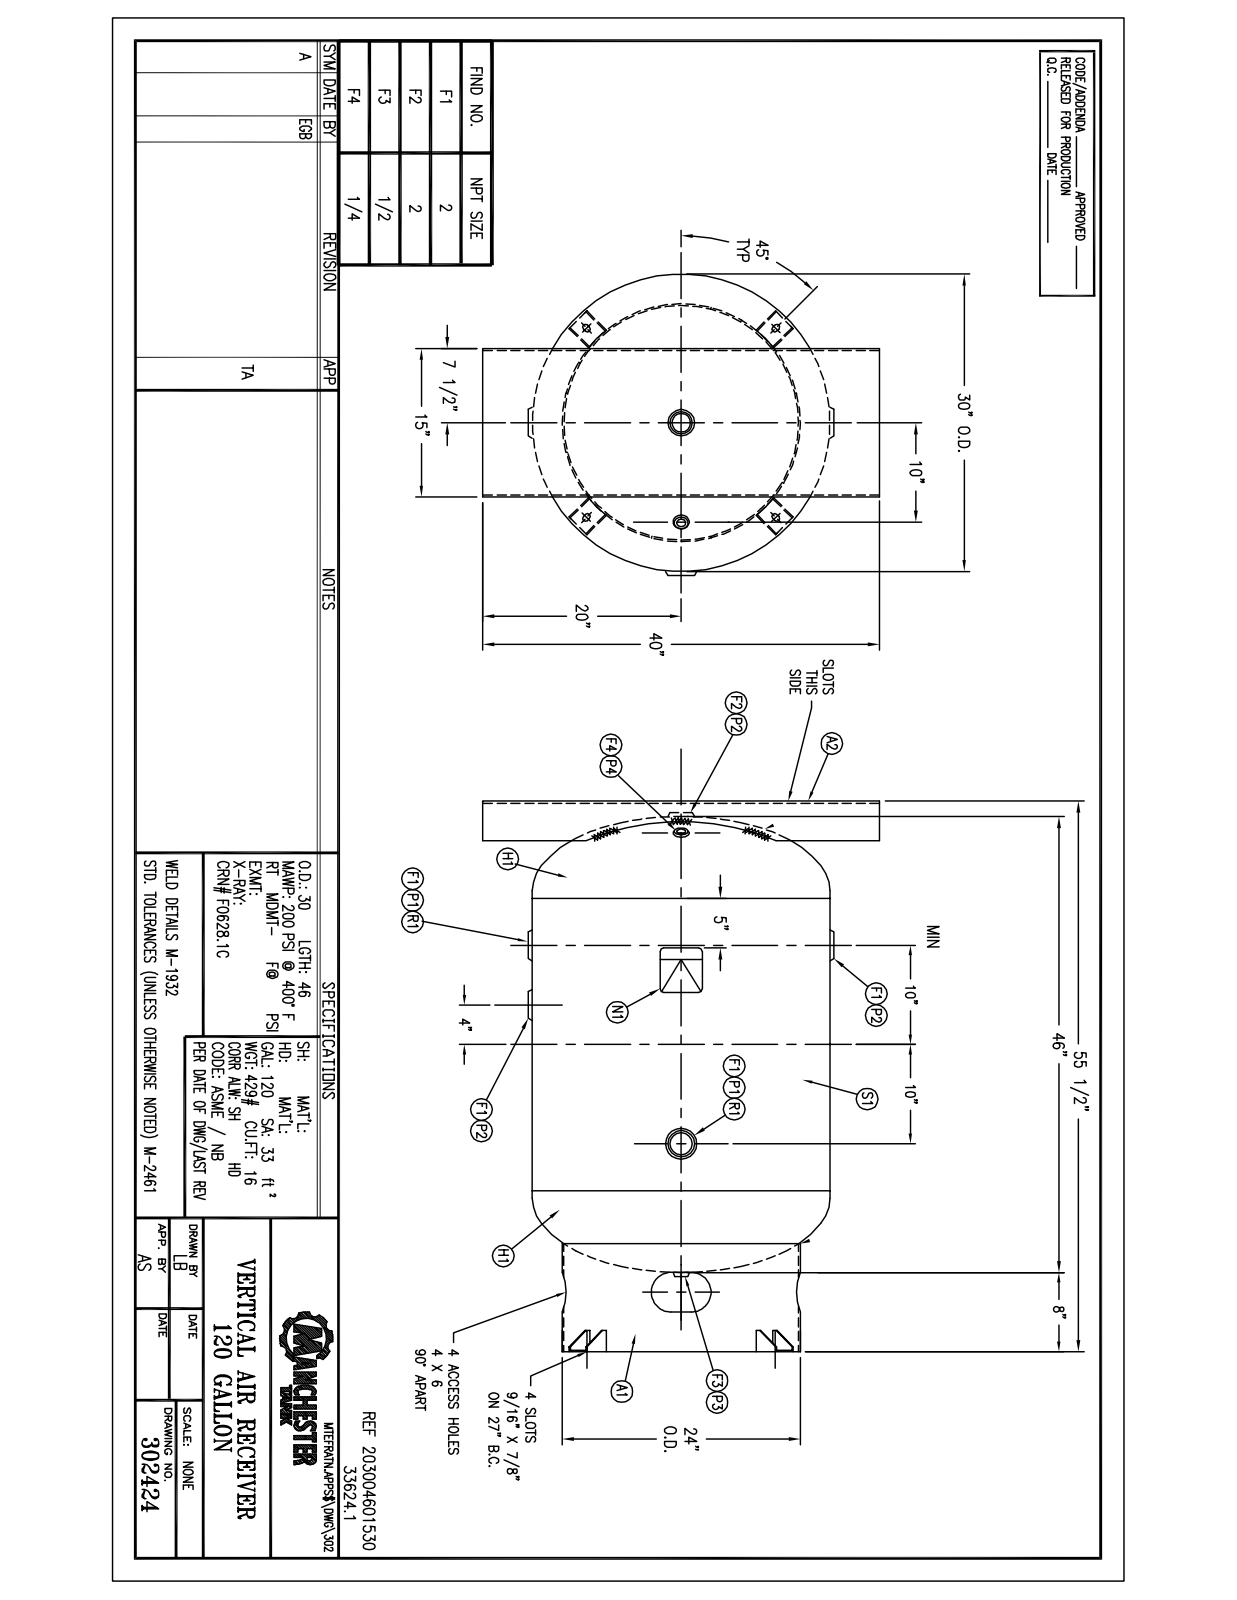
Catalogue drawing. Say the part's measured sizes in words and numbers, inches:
The part is named "302424". Its 3-D file was written by "SolidWorks 2011 (CONFIG_CONTROL_DESIGN)". It is 0 solids with 288 faces: 112 planar, 98 cylindrical and 78 other. Overall it measures 55.213 by 40 by 30.842 inches. Round holes: 2 of diameter 2.375, 2 of diameter 2.375, 1 of diameter 0.54, 1 of diameter 1, 1 of diameter 3.5, 1 of diameter 23.638, 1 of diameter 29.546. Round bosses or shafts: 3 of diameter 3.625, 1 of diameter 30, 1 of diameter 29.63, 1 of diameter 24, 1 of diameter 2.875, 1 of diameter 1.5. Partial cylindrical surfaces (rounded edges, fillets, slot ends): 10 of radius 0.266, 8 of radius 0.25, 8 of radius 0.281, 8 of radius 0.384, 2 of radius 0.094, 2 of radius 0.312, 2 of radius 0.344, 1 of radius 15. The main face-to-face distances are 0.25, 14.75, 15, 14.5, 0.134, 54.963, 55.213, 2.383, 45.338, 9.625. The hole center spacings are 6.
